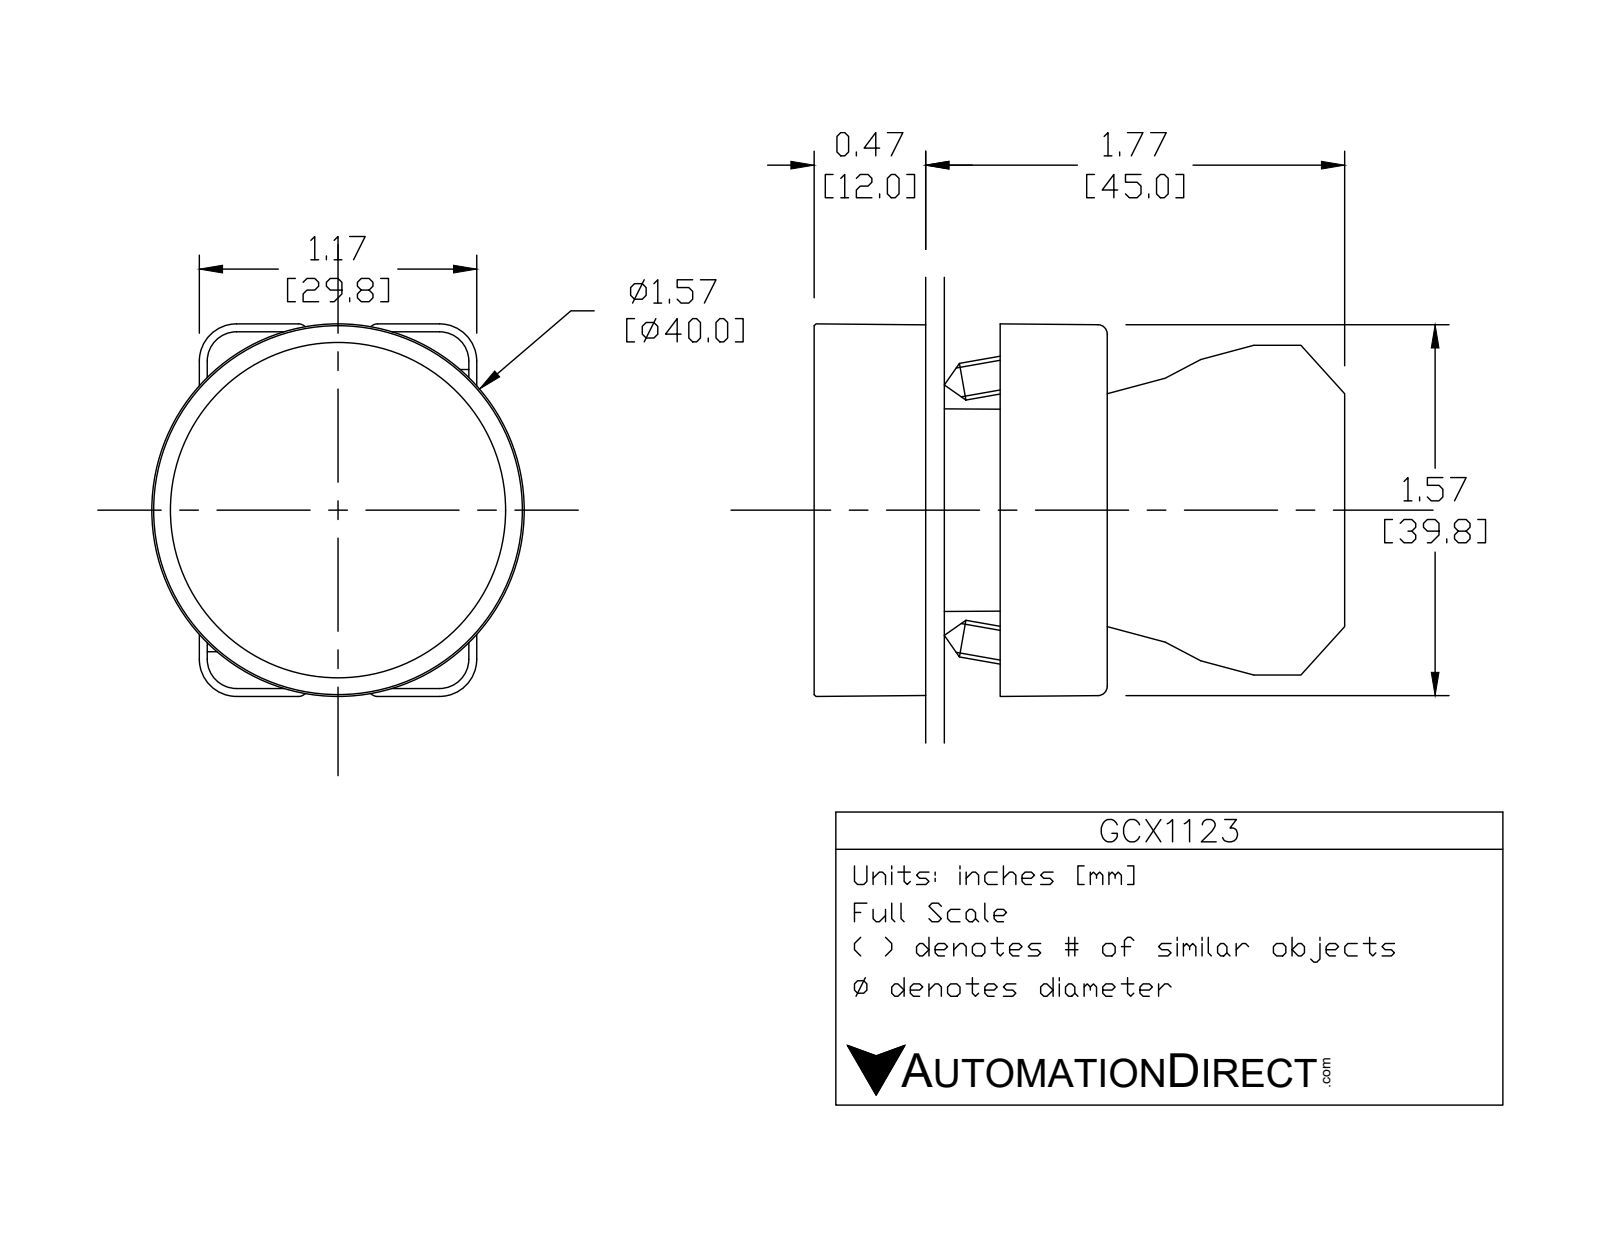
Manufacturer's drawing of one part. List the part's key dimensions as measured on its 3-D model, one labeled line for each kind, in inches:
Part name (STEP PRODUCT): ecx1040; GCX1123; GCX1123 OPERATOR; ecx1029
STEP written by: SolidWorks 2016 (AUTOMOTIVE_DESIGN)
Units: inches
Bodies: 6 solids, 381 faces (222 planar, 132 cylindrical, 27 other)
Overall size (bounding box): 2.217 × 1.581 × 1.569
Volume: 2.153 in³ · Surface area: 32.09 in²
Round holes (diameter × count): ⌀0.079 ×2, ⌀0.124 ×2, ⌀0.13 ×2, ⌀0.087 ×1, ⌀0.197 ×1, ⌀0.878 ×1, ⌀0.888 ×1, ⌀1.417 ×1
Round bosses / shafts (diameter × count): ⌀0.157 ×2, ⌀1.569 ×1, ⌀1.398 ×1, ⌀0.945 ×1, ⌀0.856 ×1, ⌀0.78 ×1
Partial cylindrical surfaces — rounded edges, fillets, slot ends (radius × count): R0.059 ×24, R0.041 ×12, R0.124 ×12, R0.157 ×12, R0.039 ×4, R0.128 ×2, R0.02 ×1, R0.063 ×1
Main face-to-face distances: 0.472, 0.72, 1.193, 0.579, 0.7, 0.02, 0.493, 0.033, 0.031, 0.689
Hole centre spacings: 0.236, 0.544, 0.472, 0.49
